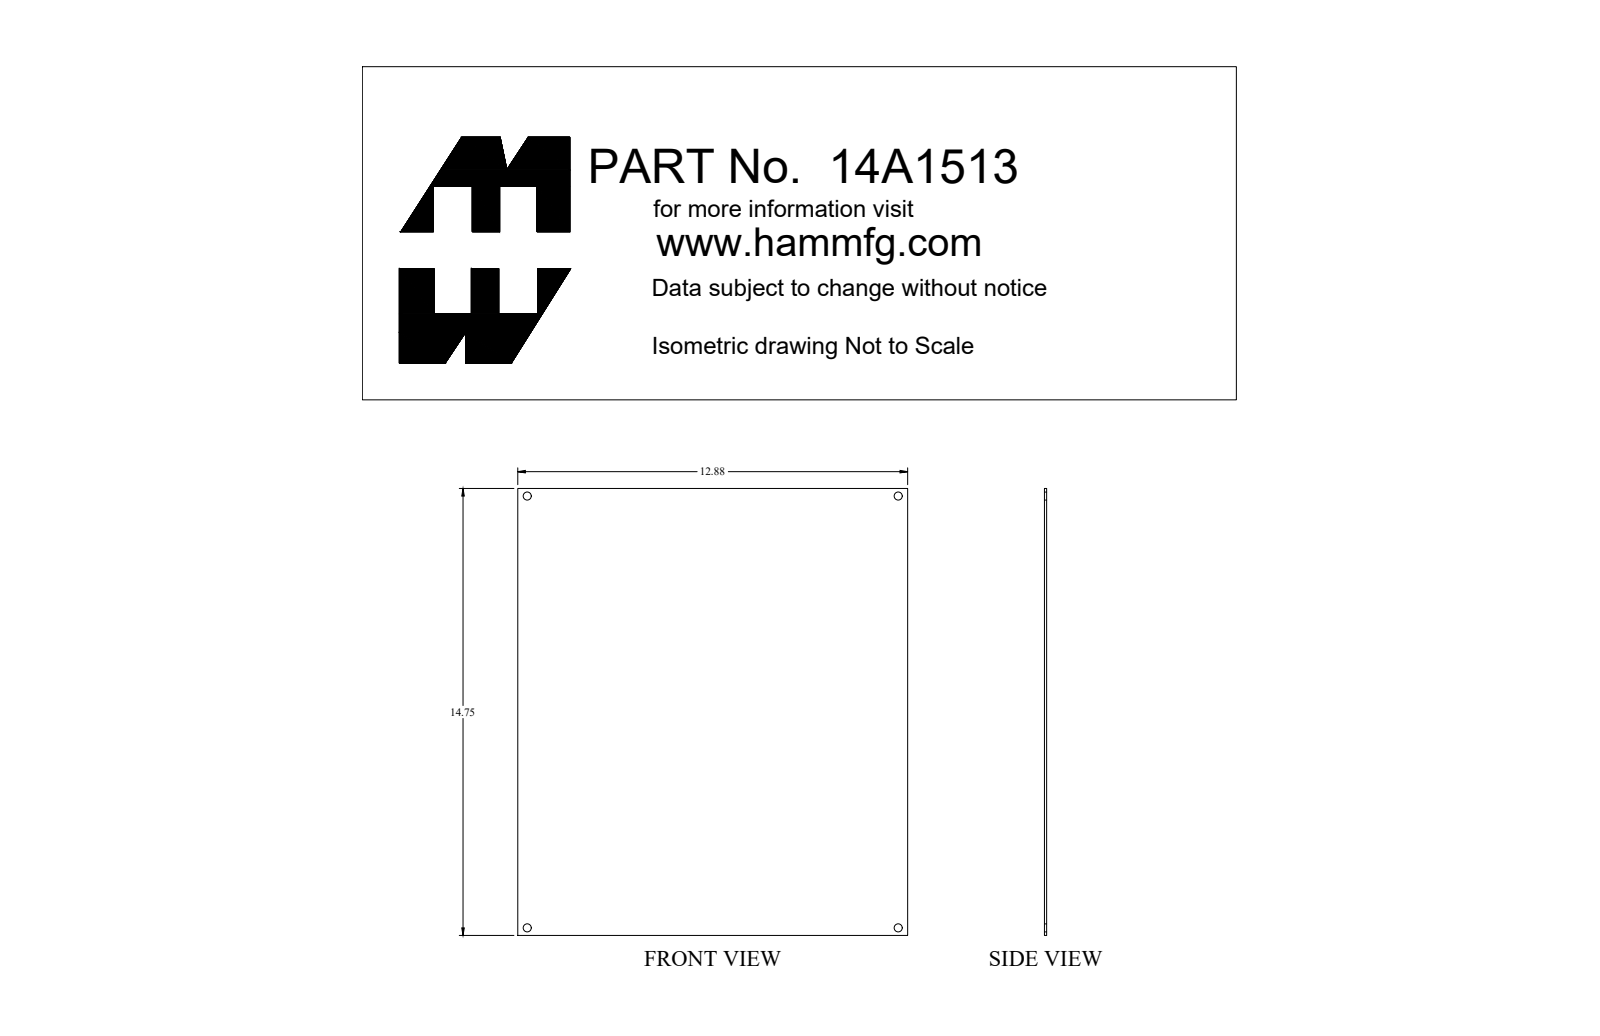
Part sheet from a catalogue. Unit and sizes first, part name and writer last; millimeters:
Units: millimetres
Overall size (bounding box): 374.7 × 327 × 1.8
Round holes (diameter × count): ⌀6.7 ×4
Main face-to-face distances: 1.8, 327, 374.7
Hole centre spacings: 311.2, 362, 477.3
Volume: 223 800 mm³ · Surface area: 247 500 mm²
Bodies: 1 solid, 10 faces (6 planar, 4 cylindrical, 0 other)
Part name (STEP PRODUCT): 14A1513
STEP written by: SolidWorks 2018 (AUTOMOTIVE_DESIGN)
